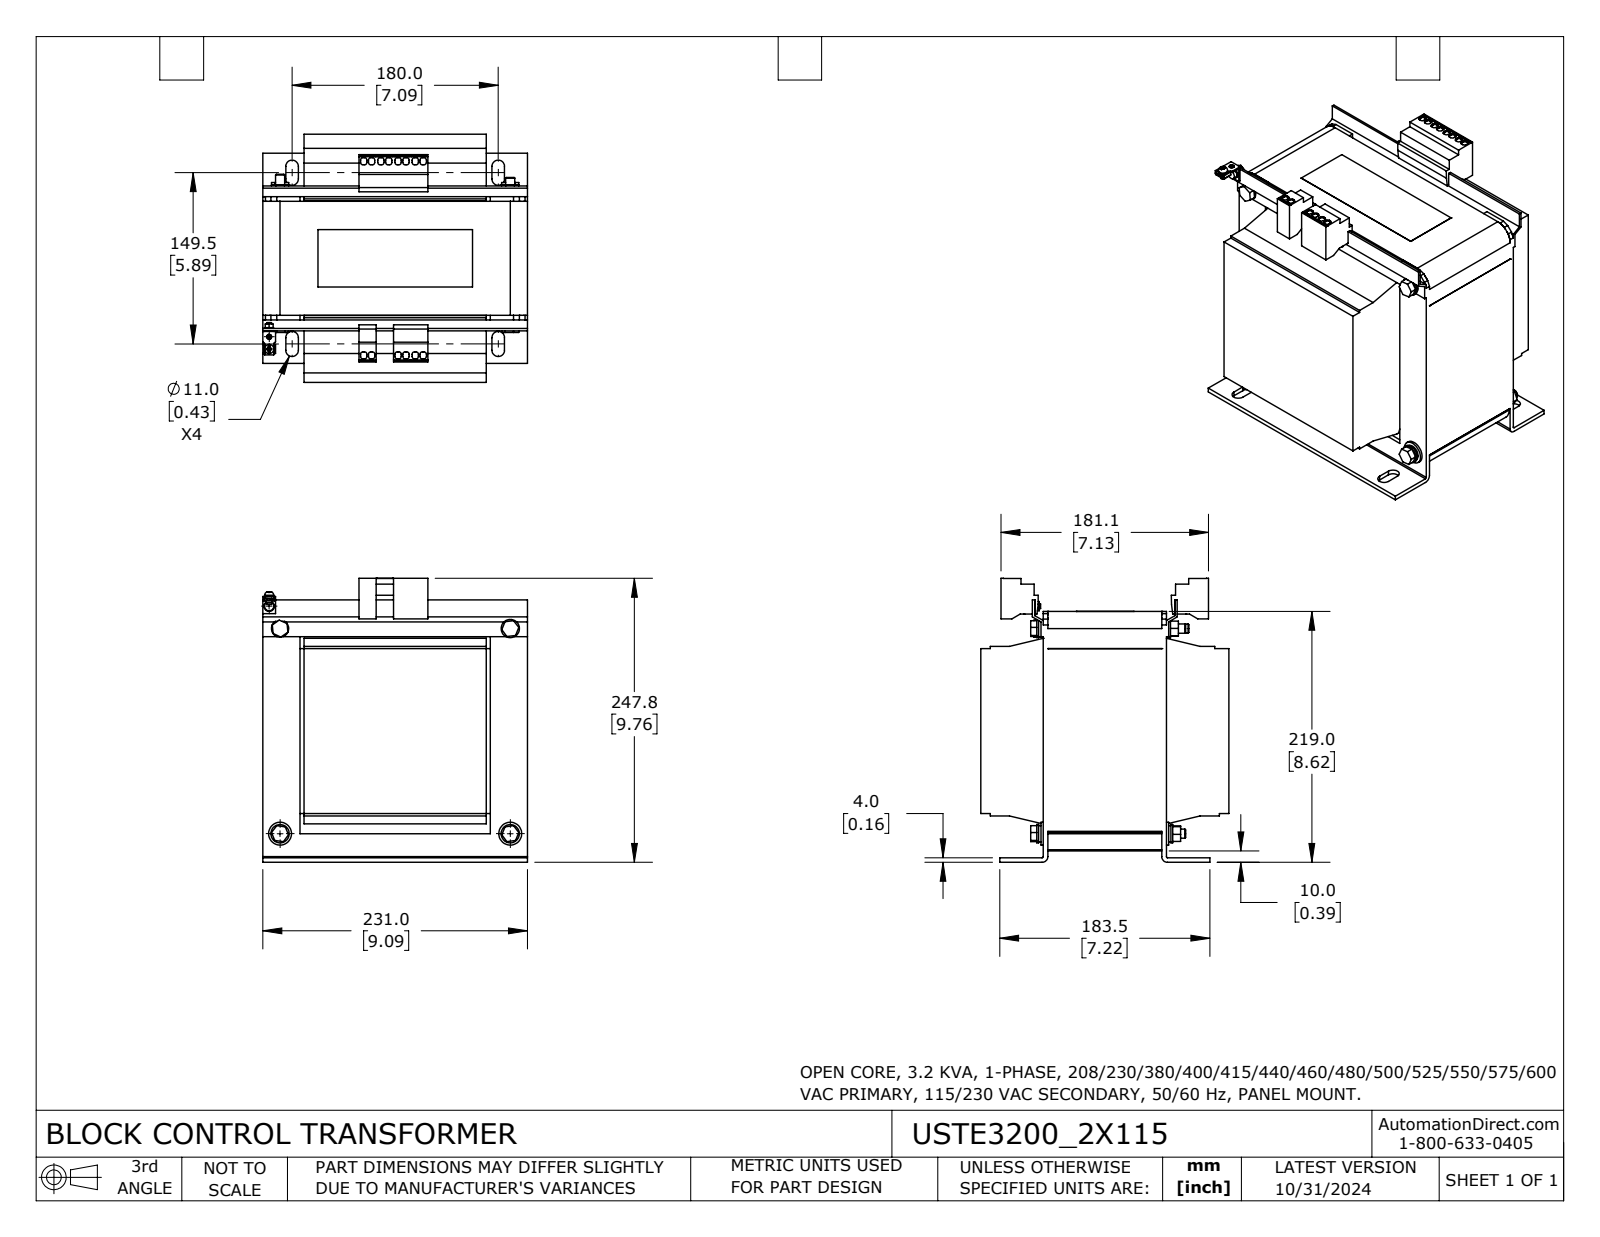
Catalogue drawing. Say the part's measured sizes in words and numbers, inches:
The part is named "USTE3200_2X115". Its 3-D file was written by "SolidWorks 2023 (CONFIG_CONTROL_DESIGN)". It is 1 solid with 757 faces: 582 planar, 159 cylindrical and 16 other. Overall it measures 9.757 by 9.094 by 8.524 inches. Its volume is 477.9 cubic inches and its surface area 778.5 square inches. Round holes: 1 of diameter 0.161, 1 of diameter 0.169. Round bosses or shafts: 6 of diameter 0.315, 4 of diameter 0.63, 3 of diameter 0.555, 2 of diameter 0.787, 2 of diameter 0.157, 1 of diameter 0.591, 1 of diameter 0.354, 1 of diameter 0.299. Partial cylindrical surfaces (rounded edges, fillets, slot ends): 56 of radius 0.087, 8 of radius 0.217, 6 of radius 0.039, 2 of radius 0.004, 2 of radius 0.043, 2 of radius 0.197, 2 of radius 0.551, 2 of radius 0.591. The main face-to-face distances are 1.28, 1.417, 7.677, 2.146, 6.378, 0.157, 6.949, 6.26, 7.815, 0.138.
